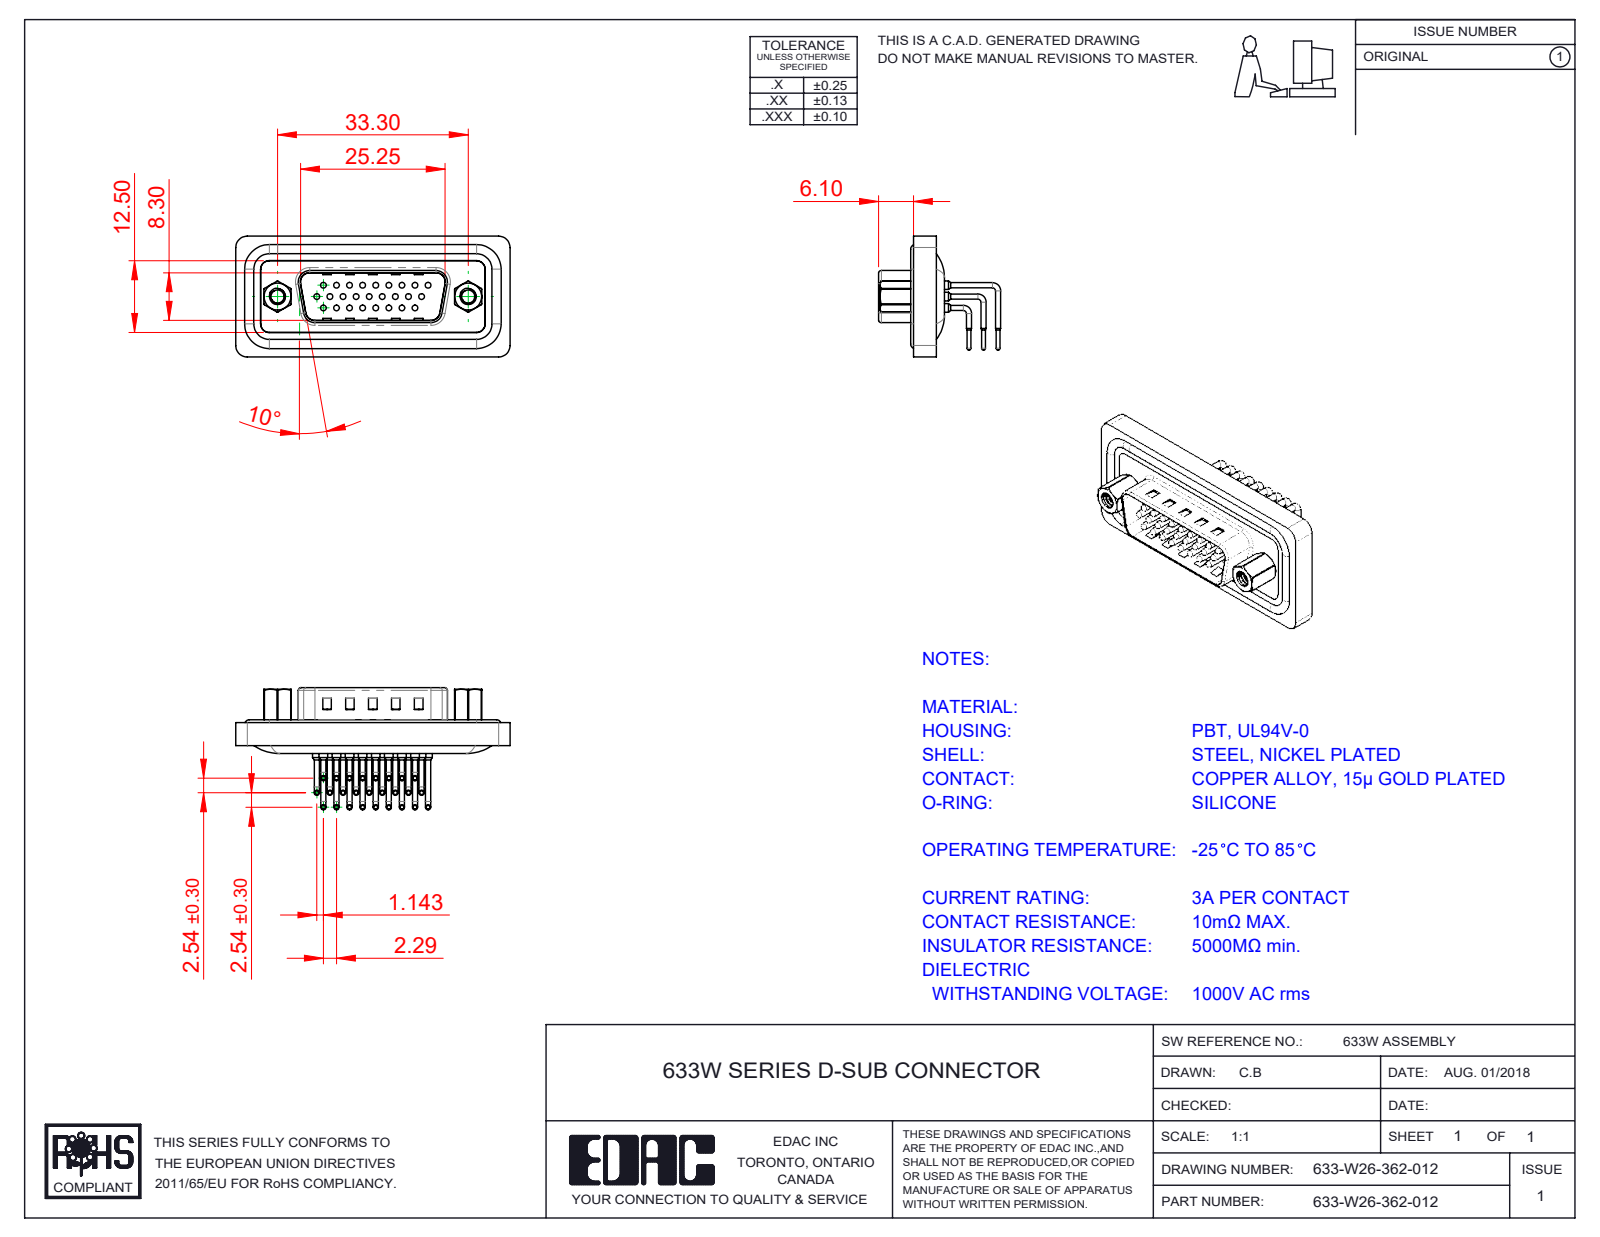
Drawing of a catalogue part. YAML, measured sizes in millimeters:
part_name: "633W 4-40 Hex Standoff; 633-W26-362-012; 633W Housing_26 Contacts; 633W Shell_26 Contacts (+5 more)"
step_written_by: "SolidWorks 2016 (CONFIG_CONTROL_DESIGN)"
units: millimeters
bodies: {solids: 34, faces: 3386, planar: 1837, cylindrical: 1194, other: 355}
overall_size: [47.89, 21.32, 21.1]
volume: 5066
surface_area: 9709
round_holes:
  - {diameter: 1, count: 26}
  - {diameter: 1.5, count: 26}
  - {diameter: 1.7, count: 26}
  - {diameter: 2, count: 26}
  - {diameter: 2.26, count: 2}
  - {diameter: 2.29, count: 2}
  - {diameter: 4, count: 2}
  - {diameter: 4.8, count: 2}
  - {diameter: 5, count: 2}
round_bosses_or_shafts:
  - {diameter: 0.9, count: 52}
  - {diameter: 1.5, count: 26}
  - {diameter: 0.65, count: 26}
  - {diameter: 1.6, count: 4}
  - {diameter: 4.9, count: 2}
  - {diameter: 2.79, count: 2}
  - {diameter: 5, count: 1}
partial_cylinders:
  - {radius: 1.01, count: 26}
  - {radius: 2, count: 16}
  - {radius: 1.5, count: 14}
  - {radius: 0.5, count: 8}
  - {radius: 2.7, count: 6}
  - {radius: 0.9, count: 4}
  - {radius: 1.6, count: 4}
  - {radius: 4.3, count: 4}
face_to_face_distances: [0.4, 1.6, 2.9, 2.5, 1.1, 0.5, 5.65, 15.45, 0.75, 4]
hole_center_spacings: [3.96, 2.28, 4.57, 6.05, 2.29, 8.24, 6.86, 6.04]
